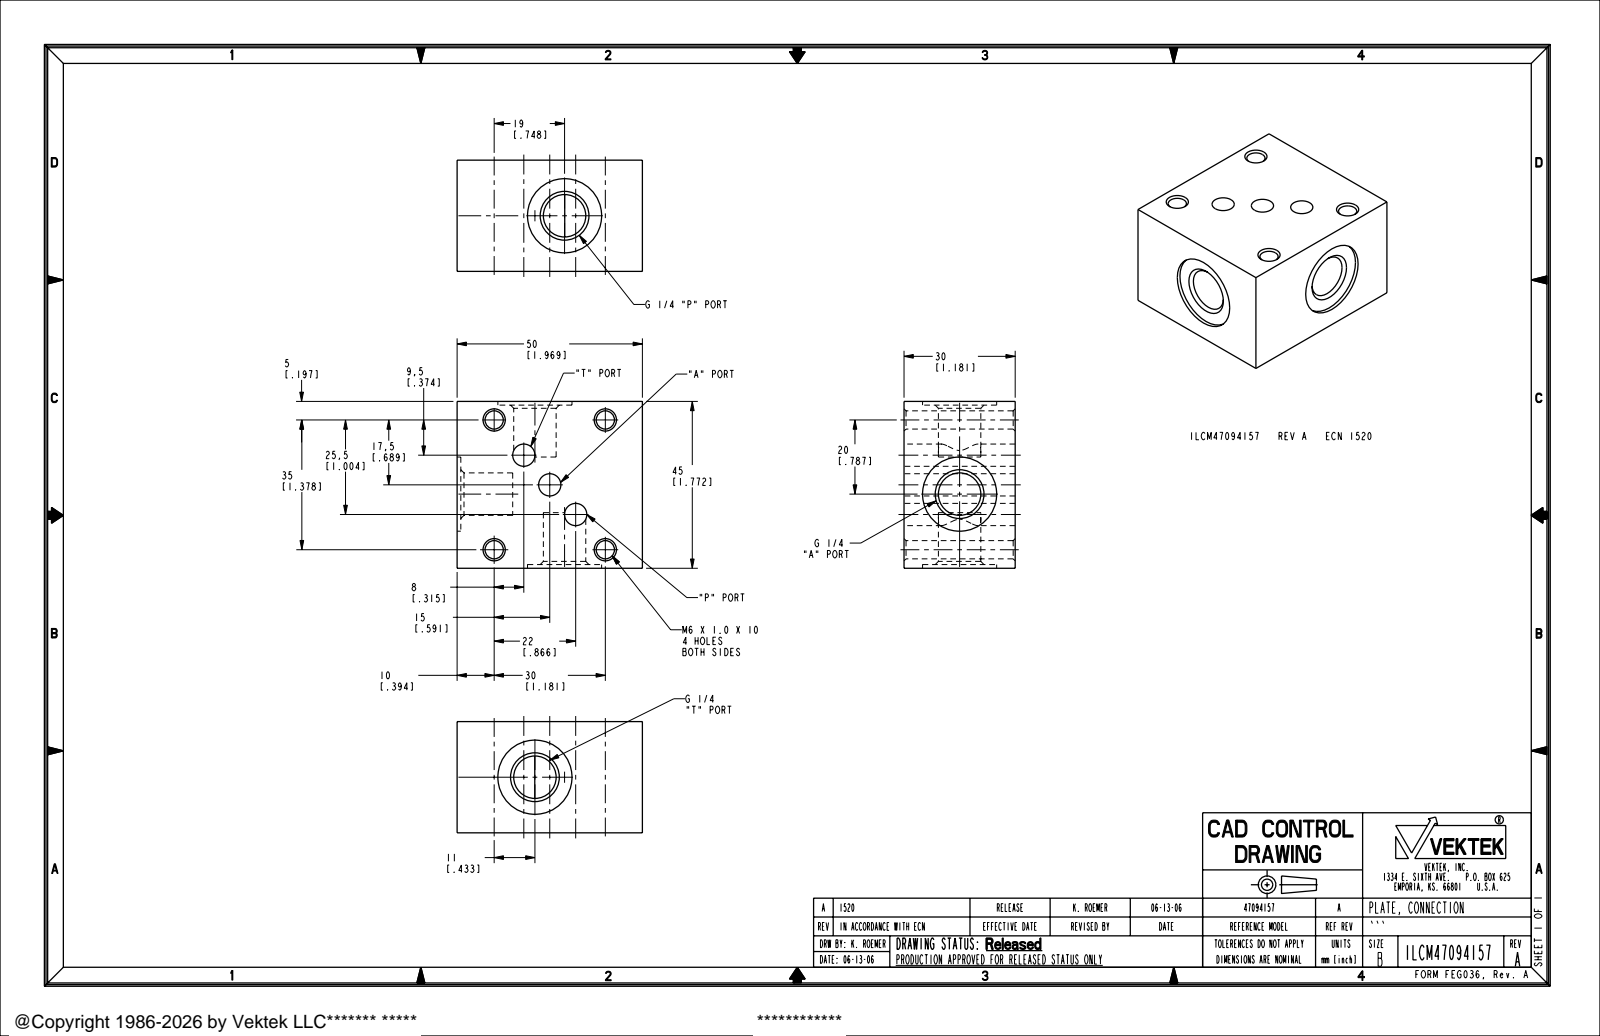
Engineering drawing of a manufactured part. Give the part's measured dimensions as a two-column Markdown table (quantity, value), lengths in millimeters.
| quantity | value |
| --- | --- |
| part name | ILCM47094157 |
| STEP written by | PRO/ENGINEER BY PARAMETRIC TECHNOLOGY CORPORATION, 2004290 (AUTOMOTIVE_DESIGN_CC2) |
| units | millimeters |
| bodies | 1 solid, 60 faces (12 planar, 26 cylindrical, 22 other) |
| overall size | 50 × 45 × 30 |
| volume | 57 656 mm³ |
| surface area | 14 680 mm² |
| round holes (diameter × count) | 4.92 × 4, 6 × 3, 11.45 × 3, 20 × 3 |
| main face-to-face distances | 30, 45, 50, 1, 44, 15, 14, 49, 43, 29 |
| hole center spacings | 23.05, 10.63, 12.42, 23.96, 26.73, 30, 33.68, 35 |
